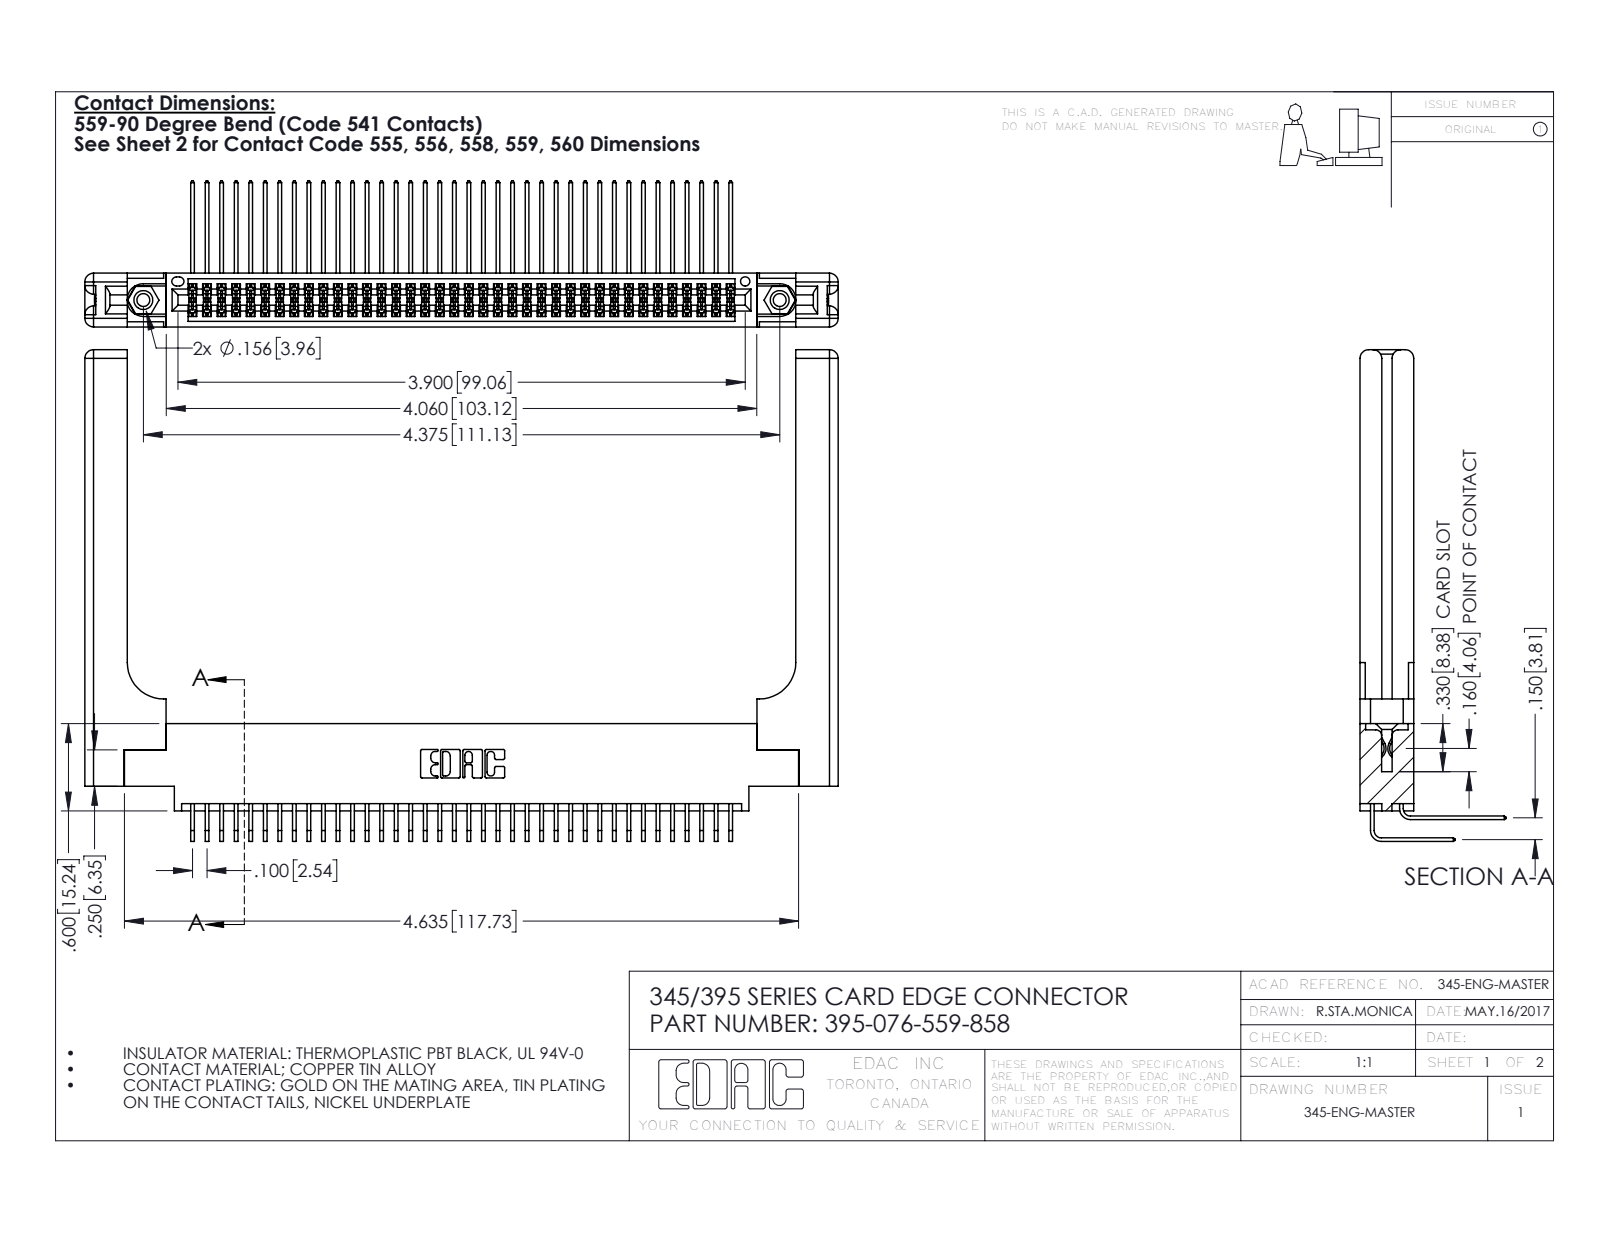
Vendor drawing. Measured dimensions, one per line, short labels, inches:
name: 345-292-001_559 Tail - 2; 345-292-001_558 559 Tail - 1; 345-250-001_345-250-001-102; 395-076-559-858 (+2 more)
written by: SolidWorks 2016 (CONFIG_CONTROL_DESIGN)
unit: in
bodies: 81 solids, 4338 faces (2892 planar, 1386 cylindrical, 60 other)
size: 5.179 × 3.379 × 1.005
volume: 1.315 in³; area: 41.08 in²
holes: 2× ⌀0.089, 2× ⌀0.125, 2× ⌀0.156, 1× ⌀0.064
bosses: 2× ⌀0.155
rounds: 114× R0.006, 22× R0.01, 16× R0.06, 6× R0.007, 6× R0.031, 3× R0.026, 2× R0.014, 2× R0.019
face distances: 0.37, 0.072, 0.298, 0.098, 0.272, 0.025, 0.2, 0.225, 0.15, 0.175
hole spacings: 0.27, 4.139, 4.375
